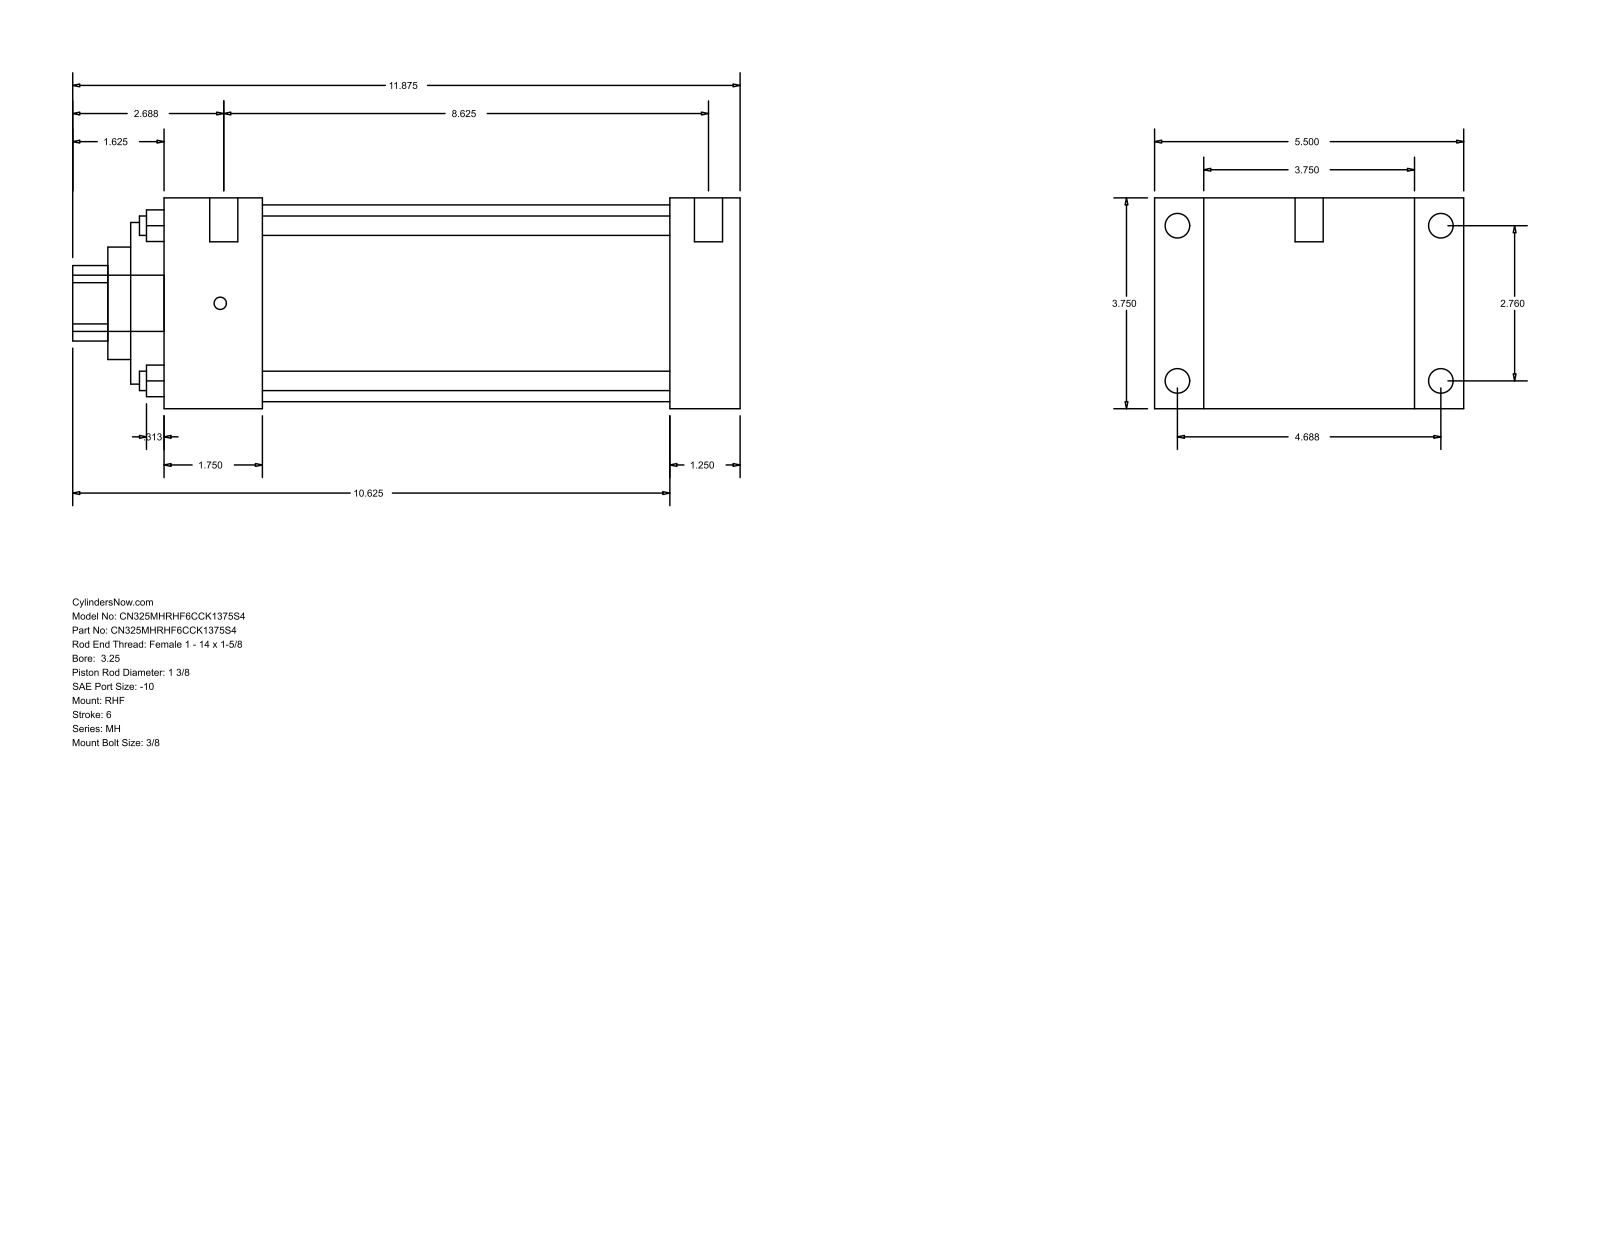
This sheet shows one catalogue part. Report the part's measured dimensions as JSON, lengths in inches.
{"part_name": "MH_RHF__0325_1.375", "step_written_by": "GSSL Pune (CONFIG_CONTROL_DESIGN)", "units": "inches", "bodies": {"solids": 0, "faces": 90, "planar": 61, "cylindrical": 29, "other": 0}, "overall_size": [11.875, 5.5, 3.75], "round_holes": [[0.345, 4], [1.375, 1], [2, 1], [2.875, 1], [3.5, 1]], "round_bosses_or_shafts": [[0.438, 4], [0.219, 4], [0.5, 2], [1, 1]], "partial_cylinders_radius": [[0.672, 1]], "face_to_face_distances": [3.75, 1.25, 0.875, 4.625, 9, 10.25, 5.5, 1.75, 7.25, 8.5], "hole_center_spacings": [1.952, 2.76, 3.903]}
